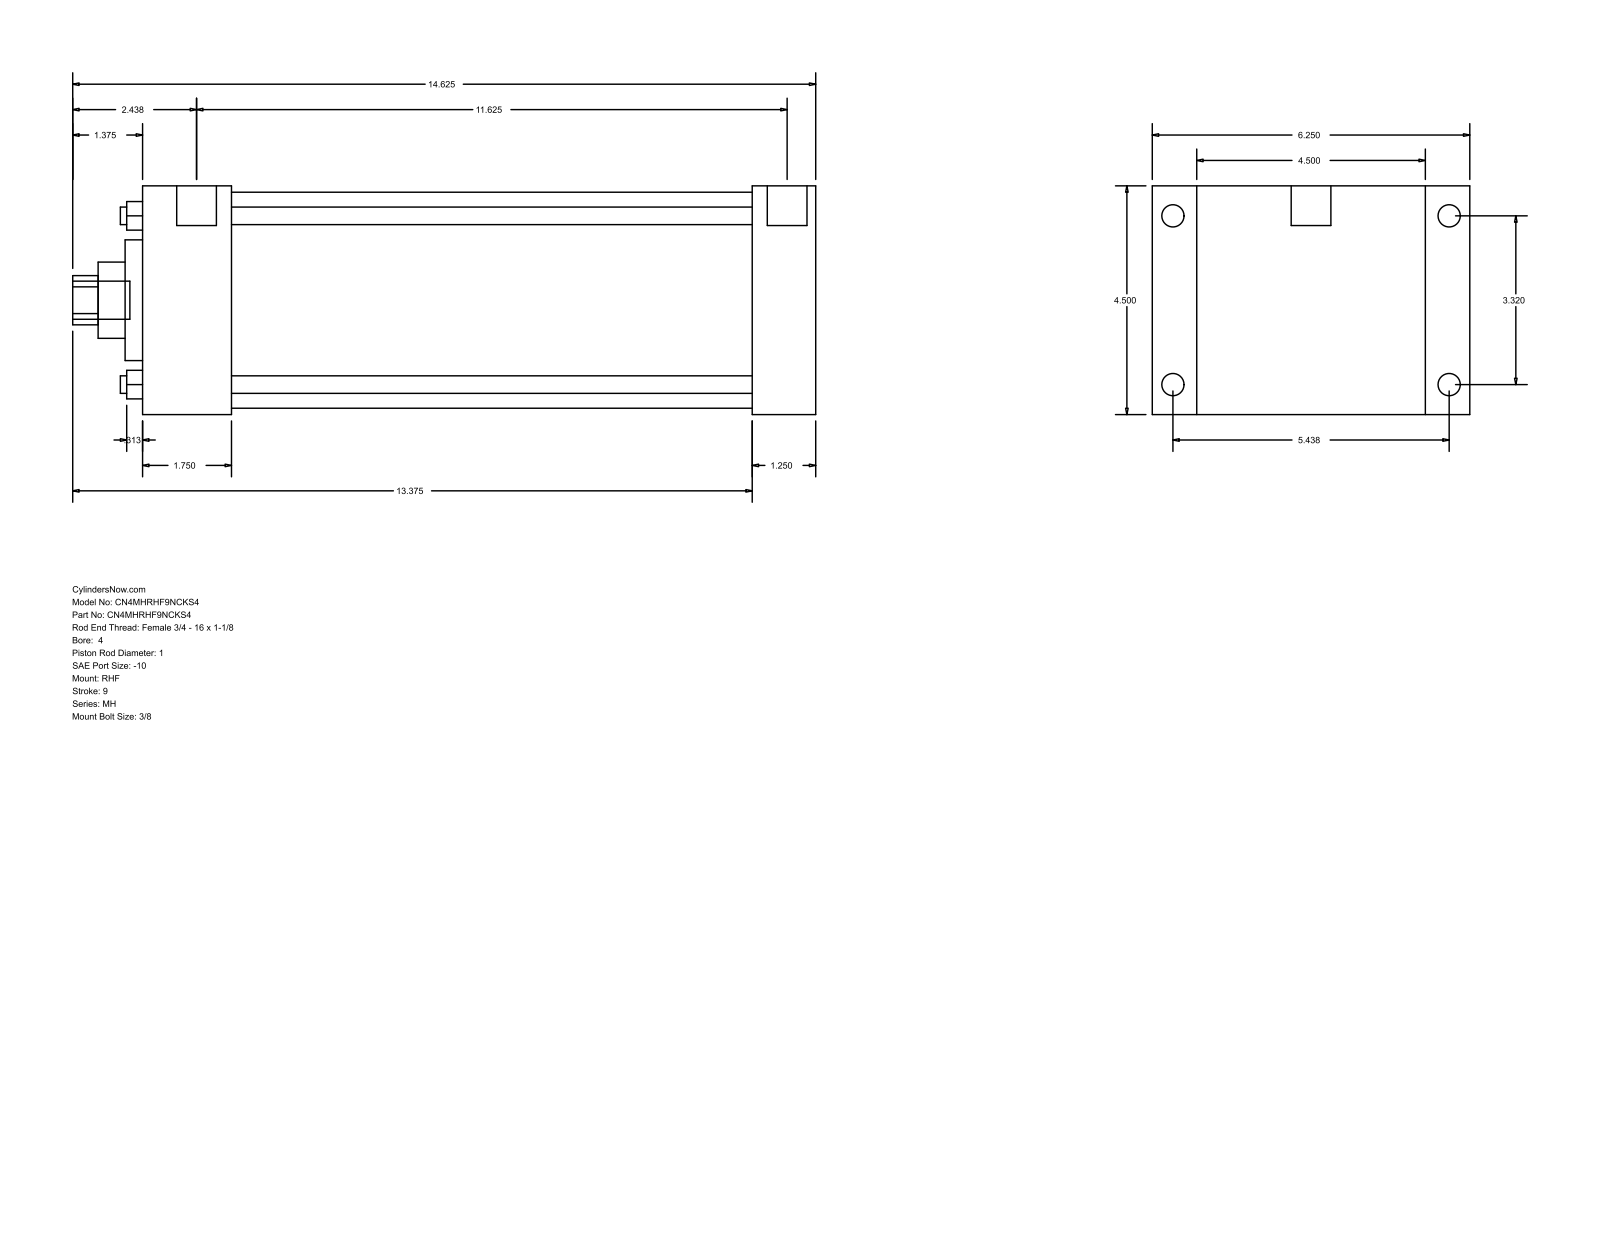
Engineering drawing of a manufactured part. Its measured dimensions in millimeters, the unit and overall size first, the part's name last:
Units: millimetres
Overall size (bounding box): 371.48 × 158.75 × 114.3
Round holes (diameter × count): ⌀8.76 ×4, ⌀25.4 ×1, ⌀38.1 ×1, ⌀60.33 ×1, ⌀107.95 ×1
Round bosses / shafts (diameter × count): ⌀11.13 ×4, ⌀8.73 ×4, ⌀19.84 ×2, ⌀19.05 ×1
Partial cylindrical surfaces — rounded edges, fillets, slot ends (radius × count): R12.29 ×1
Main face-to-face distances: 114.3, 336.56, 304.81, 31.75, 22.23, 136.53, 44.46, 260.35, 292.1, 158.76
Hole centre spacings: 59.62, 84.32, 119.25
Bodies: 0 solids, 90 faces (61 planar, 29 cylindrical, 0 other)
Part name (STEP PRODUCT): MH_RHF__0400_1
STEP written by: GSSL Pune (CONFIG_CONTROL_DESIGN)
